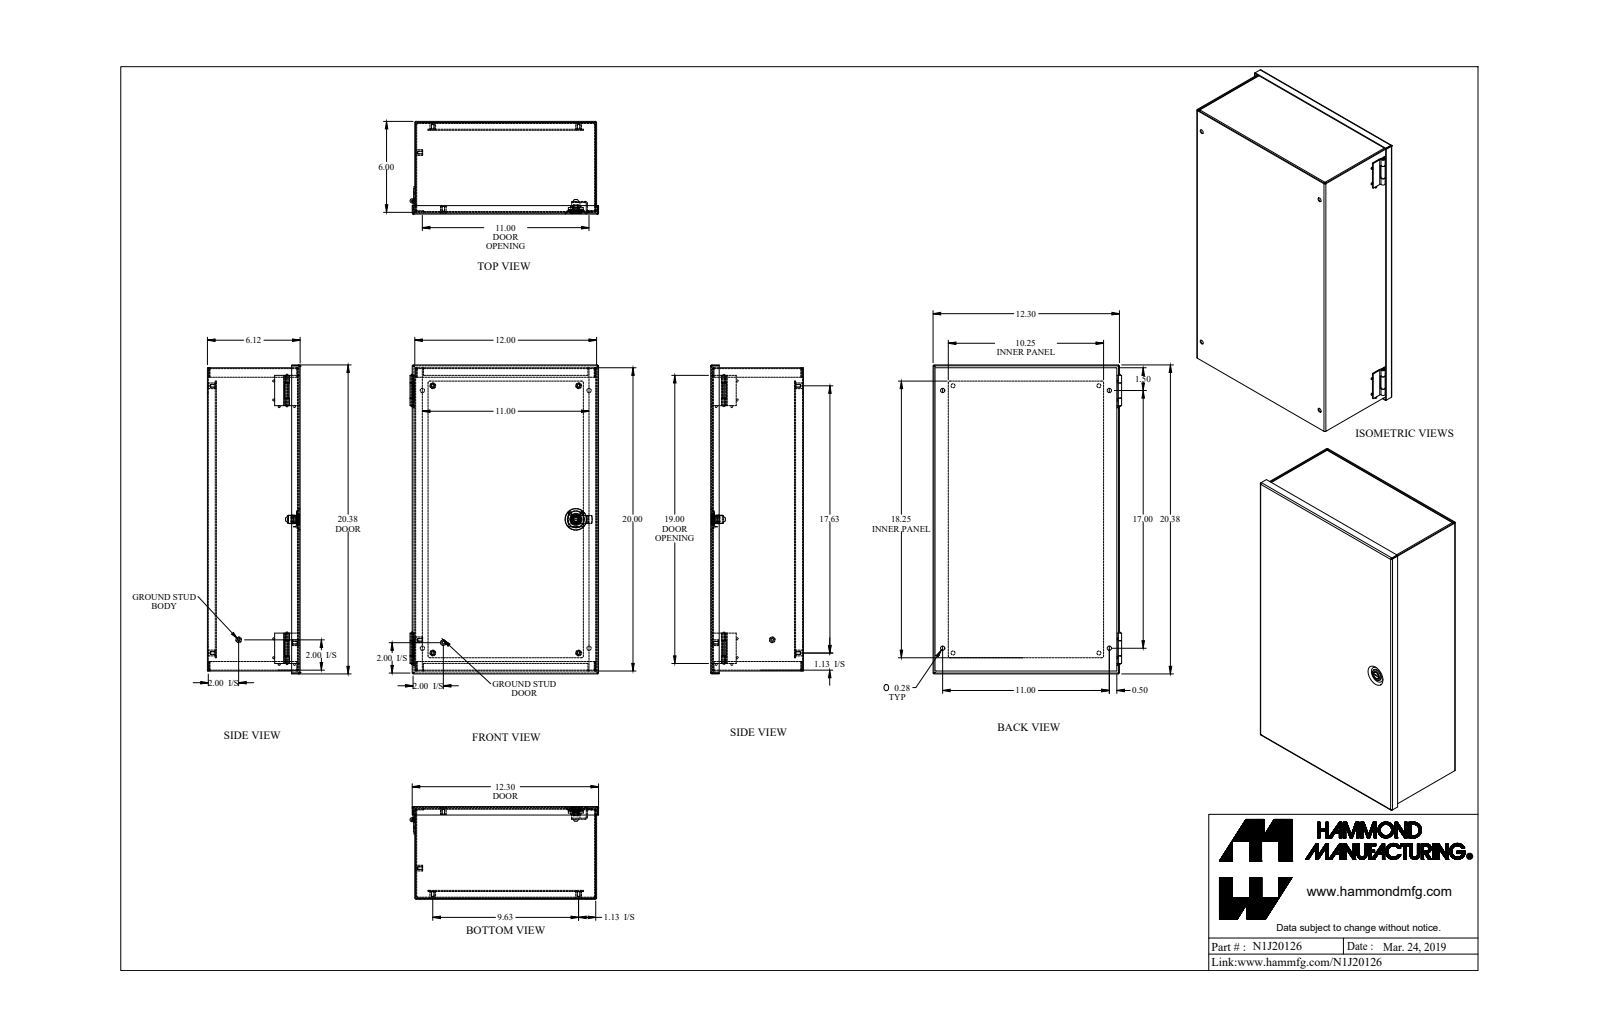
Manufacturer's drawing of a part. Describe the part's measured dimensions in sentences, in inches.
The part is named "N1J20126". Its 3-D file was written by "SolidWorks 2018 (AUTOMOTIVE_DESIGN)". It is 18 solids with 477 faces: 224 planar, 188 cylindrical and 65 other. Overall it measures 20.38 by 12.443 by 6.118 inches. Its volume is 68.78 cubic inches and its surface area 2 323 square inches. Round holes: 6 of diameter 0.156, 4 of diameter 0.265, 4 of diameter 0.28, 1 of diameter 0.125, 1 of diameter 0.319, 1 of diameter 0.476. Round bosses or shafts: 8 of diameter 0.131, 6 of diameter 0.375, 1 of diameter 0.787, 1 of diameter 0.547, 1 of diameter 0.472, 1 of diameter 0.469, 1 of diameter 0.366, 1 of diameter 0.32. Partial cylindrical surfaces (rounded edges, fillets, slot ends): 16 of radius 0.029, 16 of radius 0.086, 4 of radius 0.012, 4 of radius 0.1, 4 of radius 0.125, 2 of radius 0.036, 2 of radius 0.079, 2 of radius 0.25. The main face-to-face distances are 0.057, 6.061, 6.004, 6.118, 11.943, 0.072, 0.517, 0.46, 5.544, 5.601. The hole center spacings are 0.755, 10.317, 17.326, 20.151, 8.544, 8.815, 9.625, 11.
